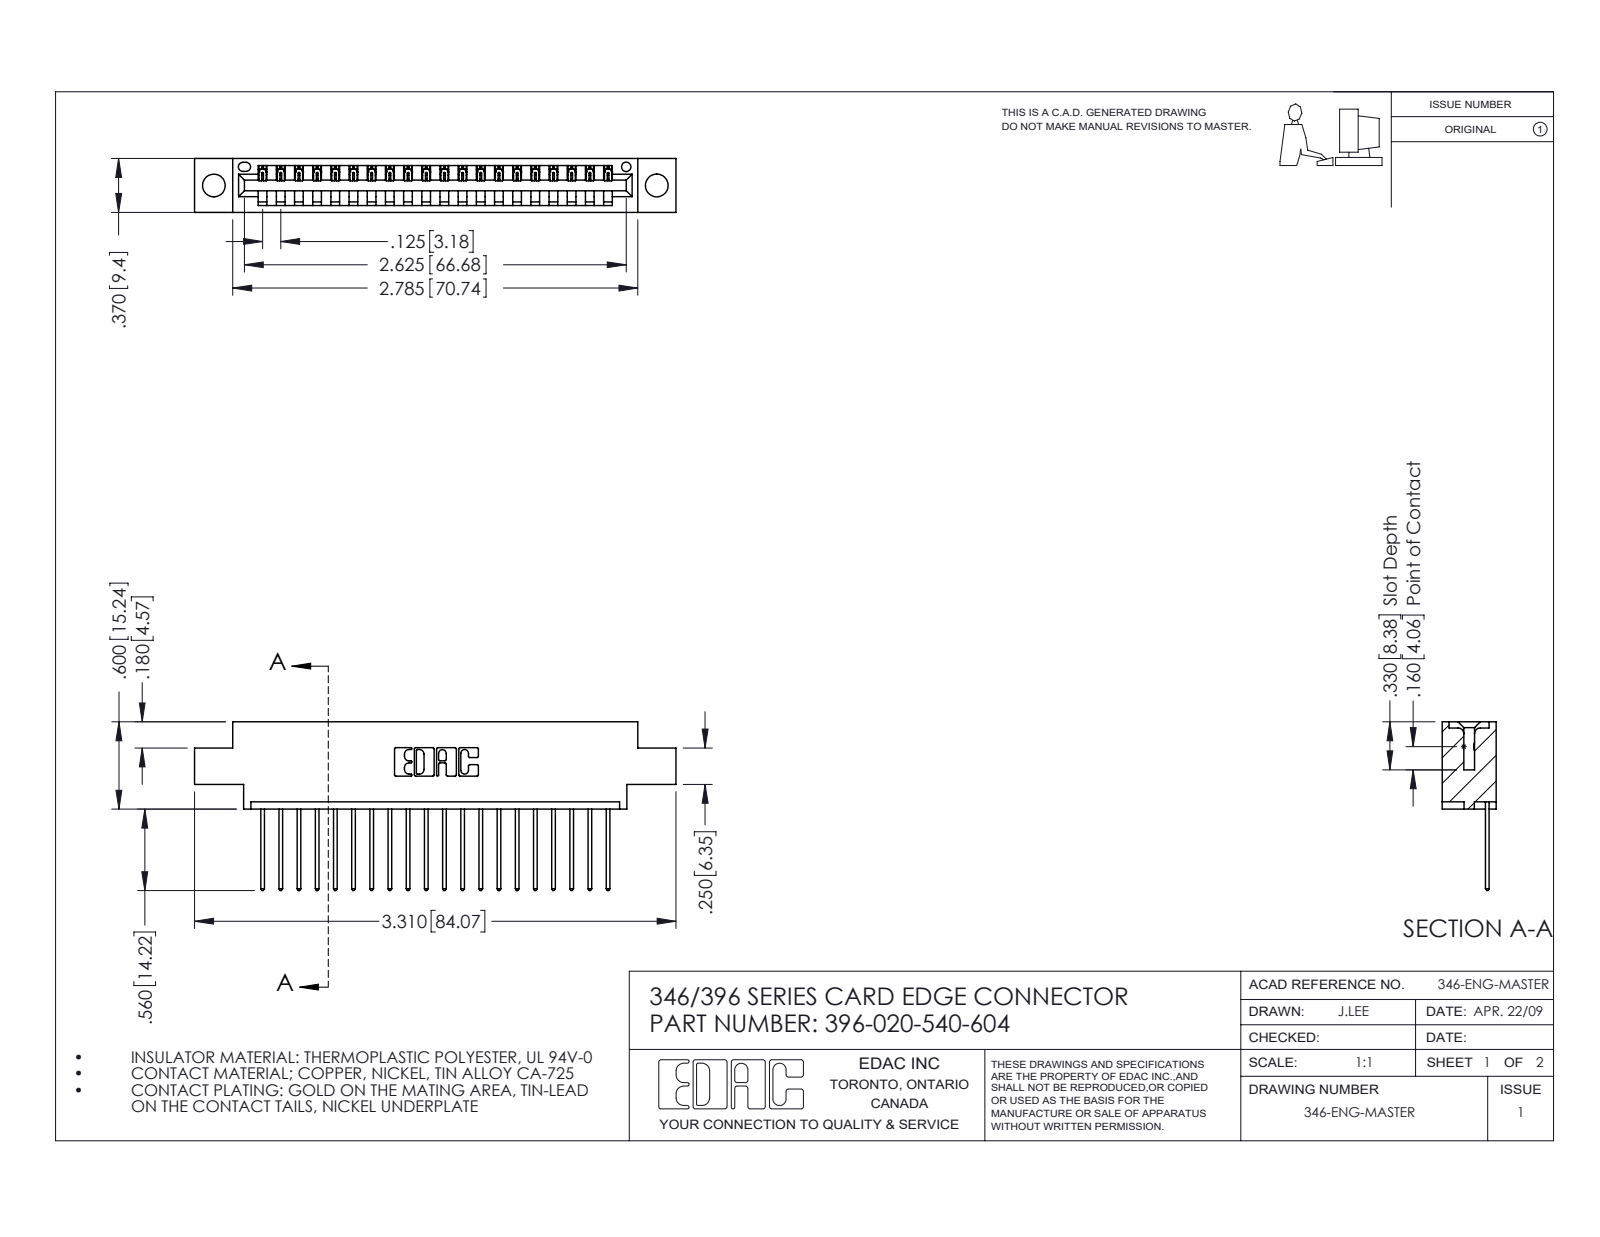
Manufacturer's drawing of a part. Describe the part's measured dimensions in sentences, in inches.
The part is named "346 Part_0.170 Offset - 0.156 Dia-TH; 396-020-540-604; 345-292-001_345-293-140". Its 3-D file was written by "SolidWorks 2016 (CONFIG_CONTROL_DESIGN)". It is 21 solids with 1286 faces: 880 planar, 406 cylindrical and 0 other. Overall it measures 3.31 by 1.16 by 0.37 inches. Its volume is 0.469 cubic inches and its surface area 14.76 square inches. Round holes: 2 of diameter 0.156, 1 of diameter 0.064. Partial cylindrical surfaces (rounded edges, fillets, slot ends): 40 of radius 0.006, 40 of radius 0.01, 22 of radius 0.01, 6 of radius 0.007, 6 of radius 0.031, 3 of radius 0.026, 2 of radius 0.031, 2 of radius 0.04. The main face-to-face distances are 0.048, 0.322, 0.37, 0.25, 0.072, 0.298, 0.025, 0.148, 0.222, 0.1. The hole center spacings are 0.246, 2.837, 3.045.
